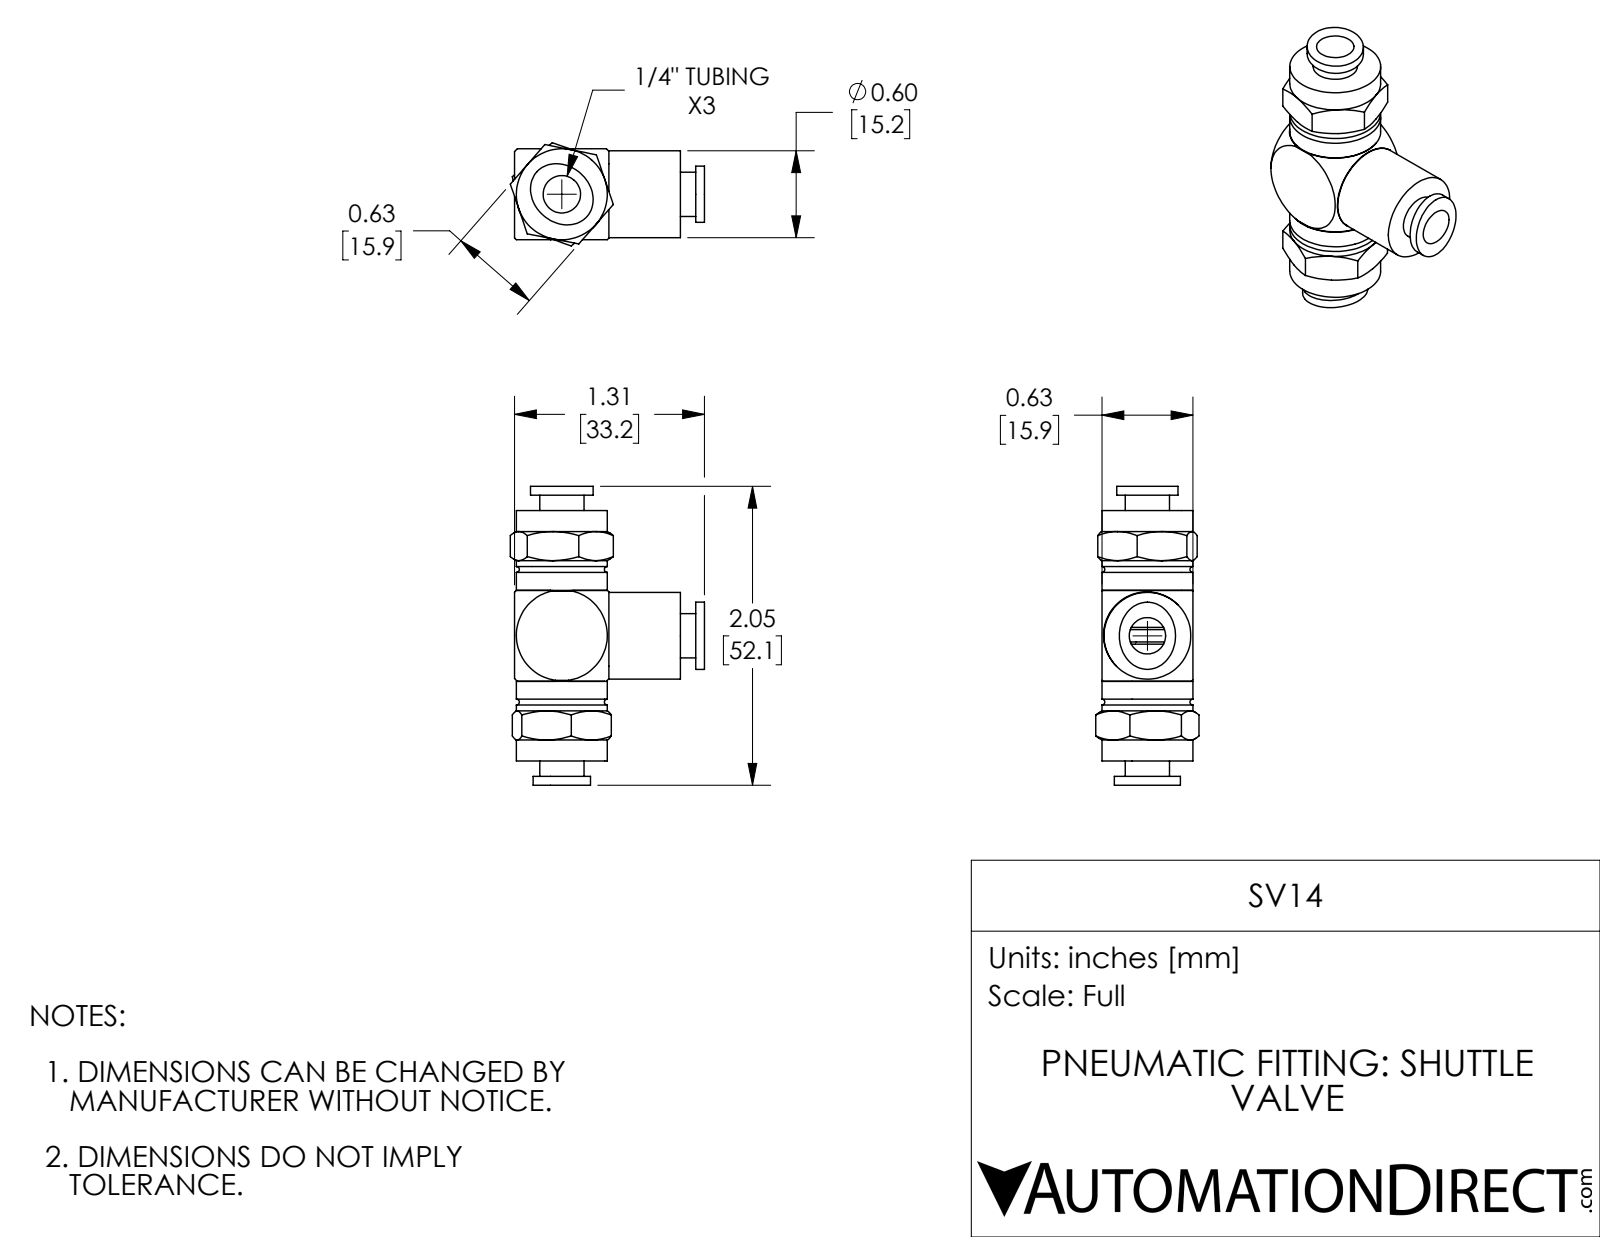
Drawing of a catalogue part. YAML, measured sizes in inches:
part_name: "SV14"
step_written_by: "SolidWorks 2018 (AUTOMOTIVE_DESIGN)"
units: inches
bodies: {solids: 3, faces: 122, planar: 34, cylindrical: 39, other: 49}
overall_size: [2.053, 1.335, 0.71]
volume: 0.639
surface_area: 11.03
round_holes:
  - {diameter: 0.25, count: 1}
  - {diameter: 0.257, count: 1}
  - {diameter: 0.437, count: 1}
round_bosses_or_shafts:
  - {diameter: 0.304, count: 2}
  - {diameter: 0.625, count: 1}
  - {diameter: 0.597, count: 1}
  - {diameter: 0.494, count: 1}
  - {diameter: 0.439, count: 1}
partial_cylinders:
  - {radius: 0.437, count: 1}
face_to_face_distances: [0.625, 0.27, 0.355, 0.548, 1.173, 1.721, 1.173, 0.548, 1.14, 0.166]
